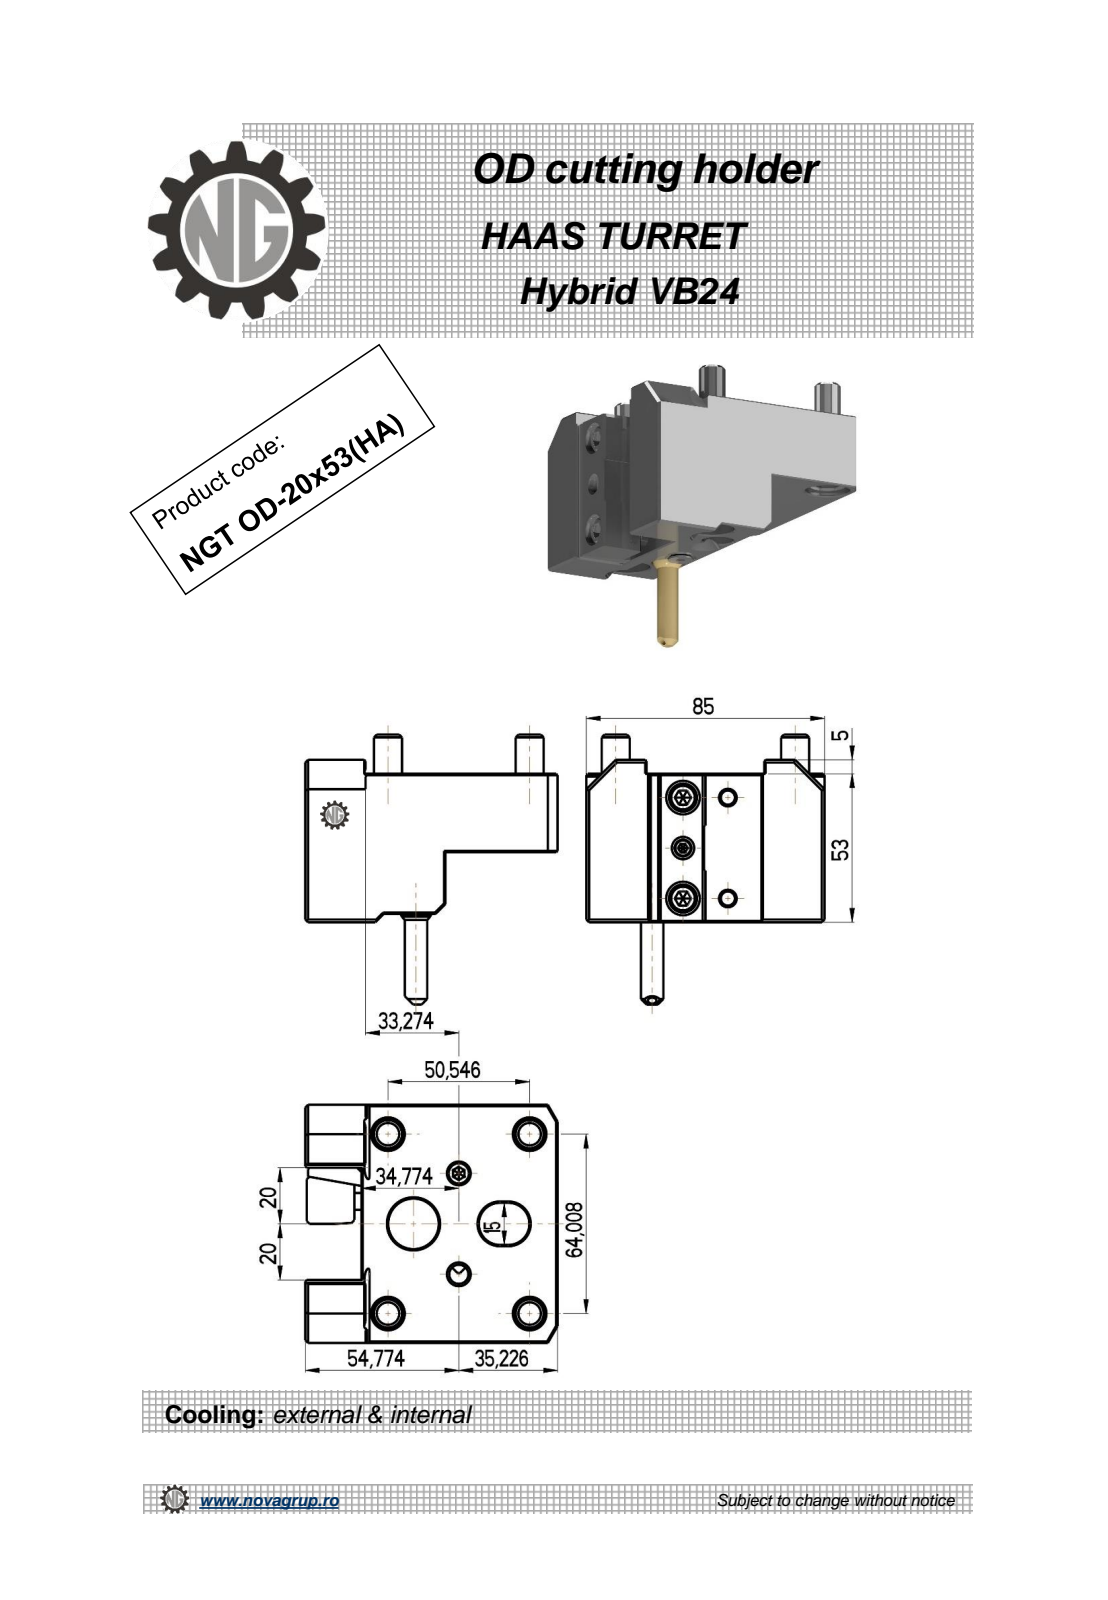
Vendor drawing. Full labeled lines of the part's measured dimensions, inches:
Part name (STEP PRODUCT): NGT_OD_20_53_HA
STEP written by: PRO/ENGINEER BY PARAMETRIC TECHNOLOGY CORPORATION, 2010280 (CONFIG_CONTROL_DESIGN)
Units: inches
Bodies: 1 solid, 209 faces (131 planar, 41 cylindrical, 37 other)
Overall size (bounding box): 3.793 × 3.543 × 3.346
Volume: 17.92 in³ · Surface area: 59.03 in²
Round holes (diameter × count): ⌀0.118 ×1, ⌀0.197 ×1, ⌀0.268 ×1, ⌀0.709 ×1
Round bosses / shafts (diameter × count): ⌀0.394 ×5, ⌀0.236 ×3, ⌀0.315 ×1
Partial cylindrical surfaces — rounded edges, fillets, slot ends (radius × count): R0.008 ×6, R0.016 ×6, R0.295 ×2, R0.039 ×1
Main face-to-face distances: 3.346, 1.102, 1.969, 0.787, 3.543, 2.756, 1.575, 1.181, 0.866, 2.087
Hole centre spacings: 0.749, 0.953, 1.576
